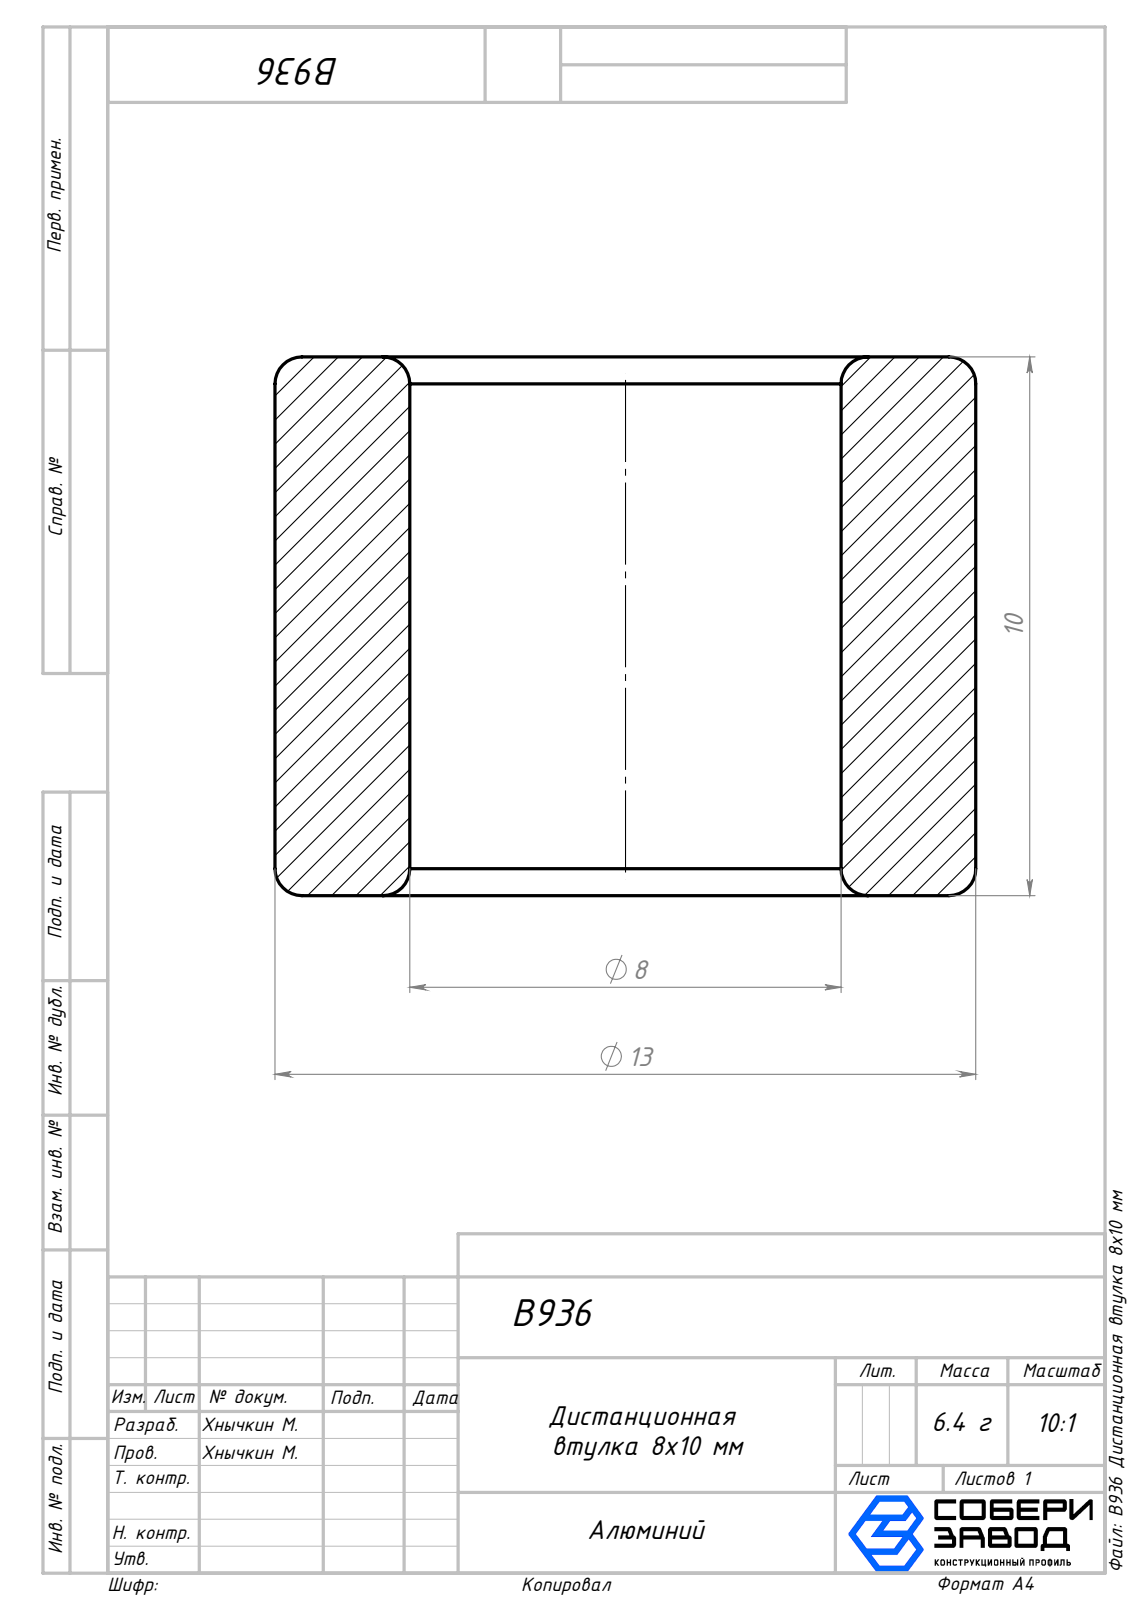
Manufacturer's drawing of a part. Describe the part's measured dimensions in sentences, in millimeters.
The part is named "B936 Дистанционная втулка 8x10 мм". Its 3-D file was written by "SolidWorks 2026 (AUTOMOTIVE_DESIGN)". It is 1 solid with 14 faces: 2 planar, 4 cylindrical and 8 other. Overall it measures 13 by 13 by 10 millimeters. Its volume is 818 cubic millimeters and its surface area 796 square millimeters. Round holes: 1 of diameter 8. Round bosses or shafts: 1 of diameter 13. The main face-to-face distances are 10.
